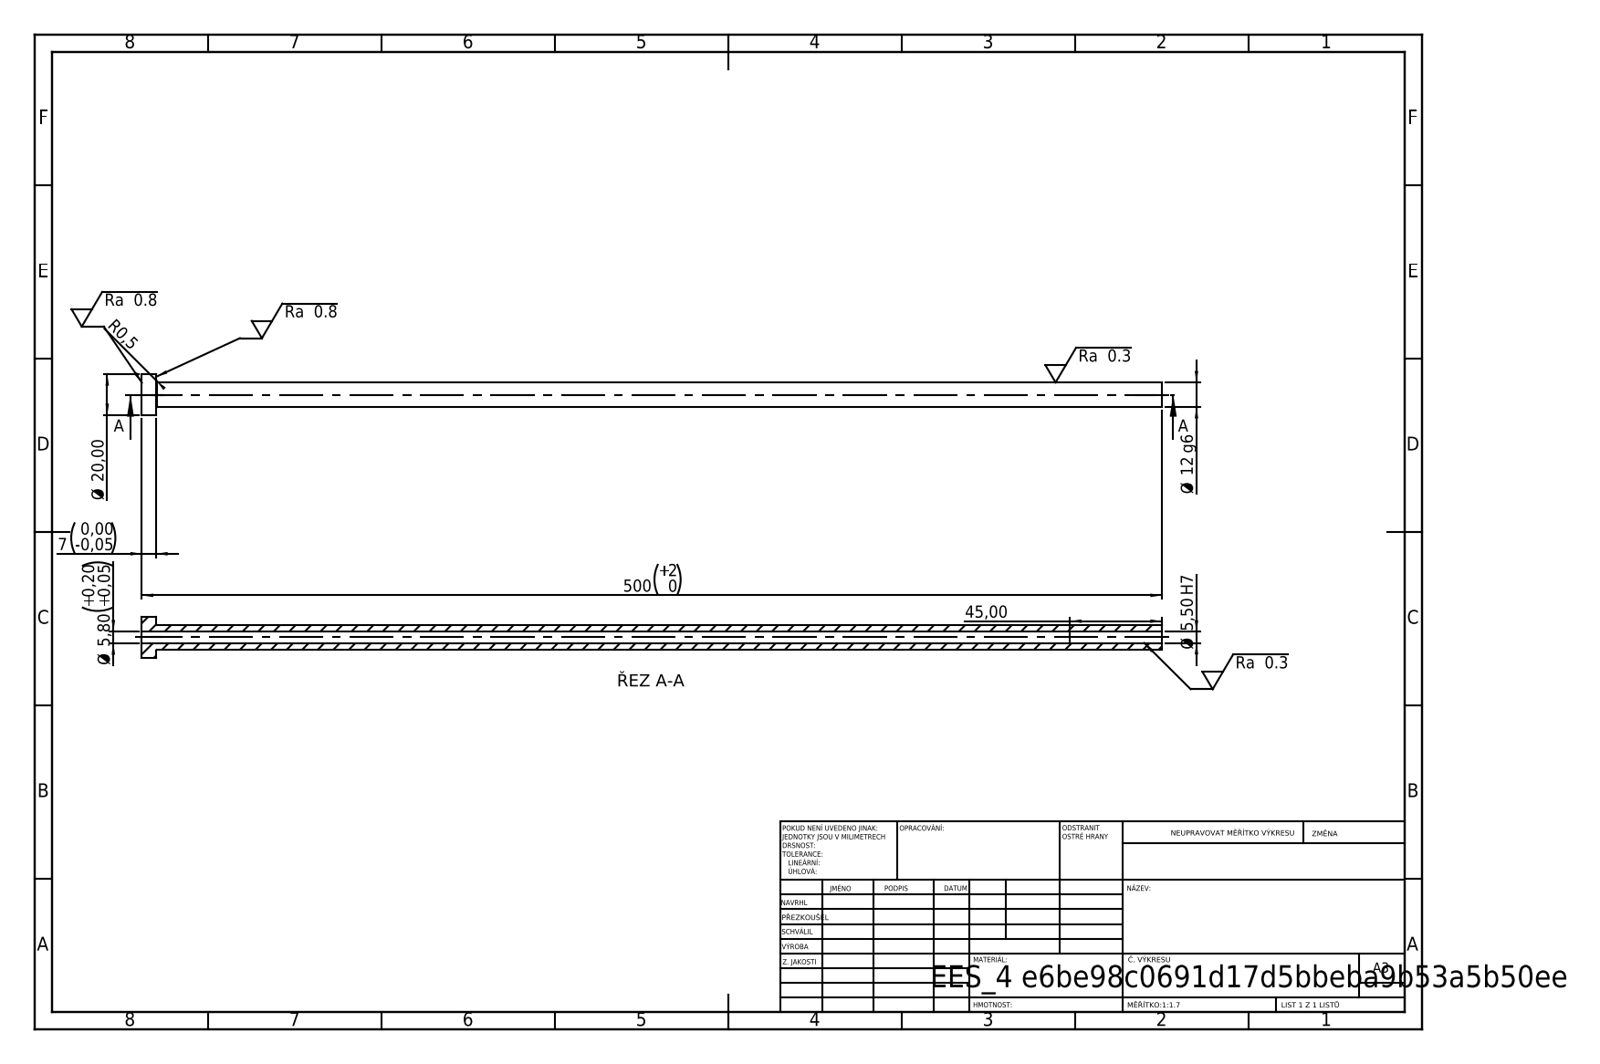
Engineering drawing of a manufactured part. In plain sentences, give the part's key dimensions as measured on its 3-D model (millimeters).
Its 3-D file was written by "SolidWorks 2019 (CONFIG_CONTROL_DESIGN)". It is 1 solid with 14 faces: 4 planar, 8 cylindrical and 2 other. Overall it measures 500 by 20 by 20 millimeters. Its volume is 44 868 cubic millimeters and its surface area 28 667 square millimeters. Round holes: 1 of diameter 5.5, 1 of diameter 5.8. Round bosses or shafts: 1 of diameter 20, 1 of diameter 12. The main face-to-face distances are 7, 500, 493, 455, 448, 45.
